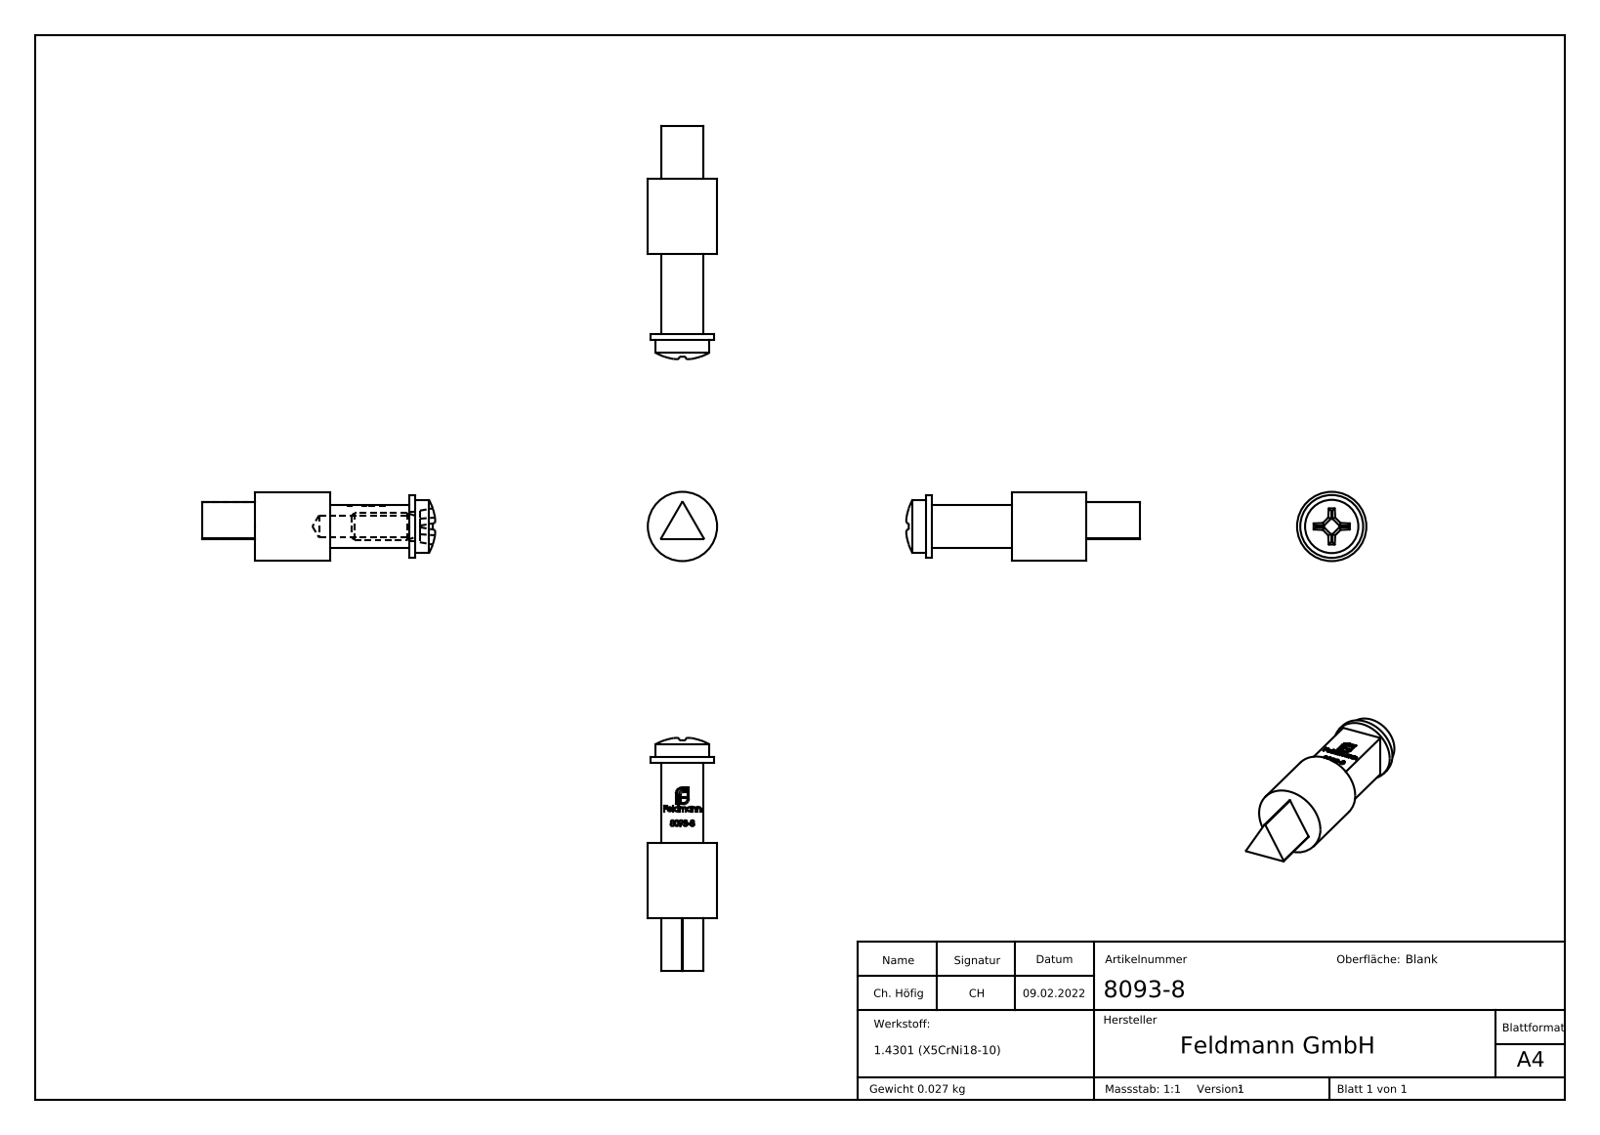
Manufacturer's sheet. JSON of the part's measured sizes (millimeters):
{"part_name": "DIN 7045_M5x12; 8093-XX Teil2; 8093-XX Teil1_8093-8 Teil1; 8093-8 (+3 more)", "step_written_by": "SolidWorks 2018 (CONFIG_CONTROL_DESIGN)", "units": "millimeters", "bodies": {"solids": 3, "faces": 302, "planar": 142, "cylindrical": 16, "other": 144}, "overall_size": [43.77, 13, 13], "volume_mm3": 3375, "surface_area_mm2": 2497, "round_holes": [[4.2, 1], [5.4, 1]], "round_bosses_or_shafts": [[13, 1], [11.8, 1], [10, 1], [5, 1]], "partial_cylinders_radius": [[0.1, 3]], "face_to_face_distances": [7.9, 1.1, 30.1, 29, 1.6, 6.3, 16.1, 15, 14, 40.1]}
